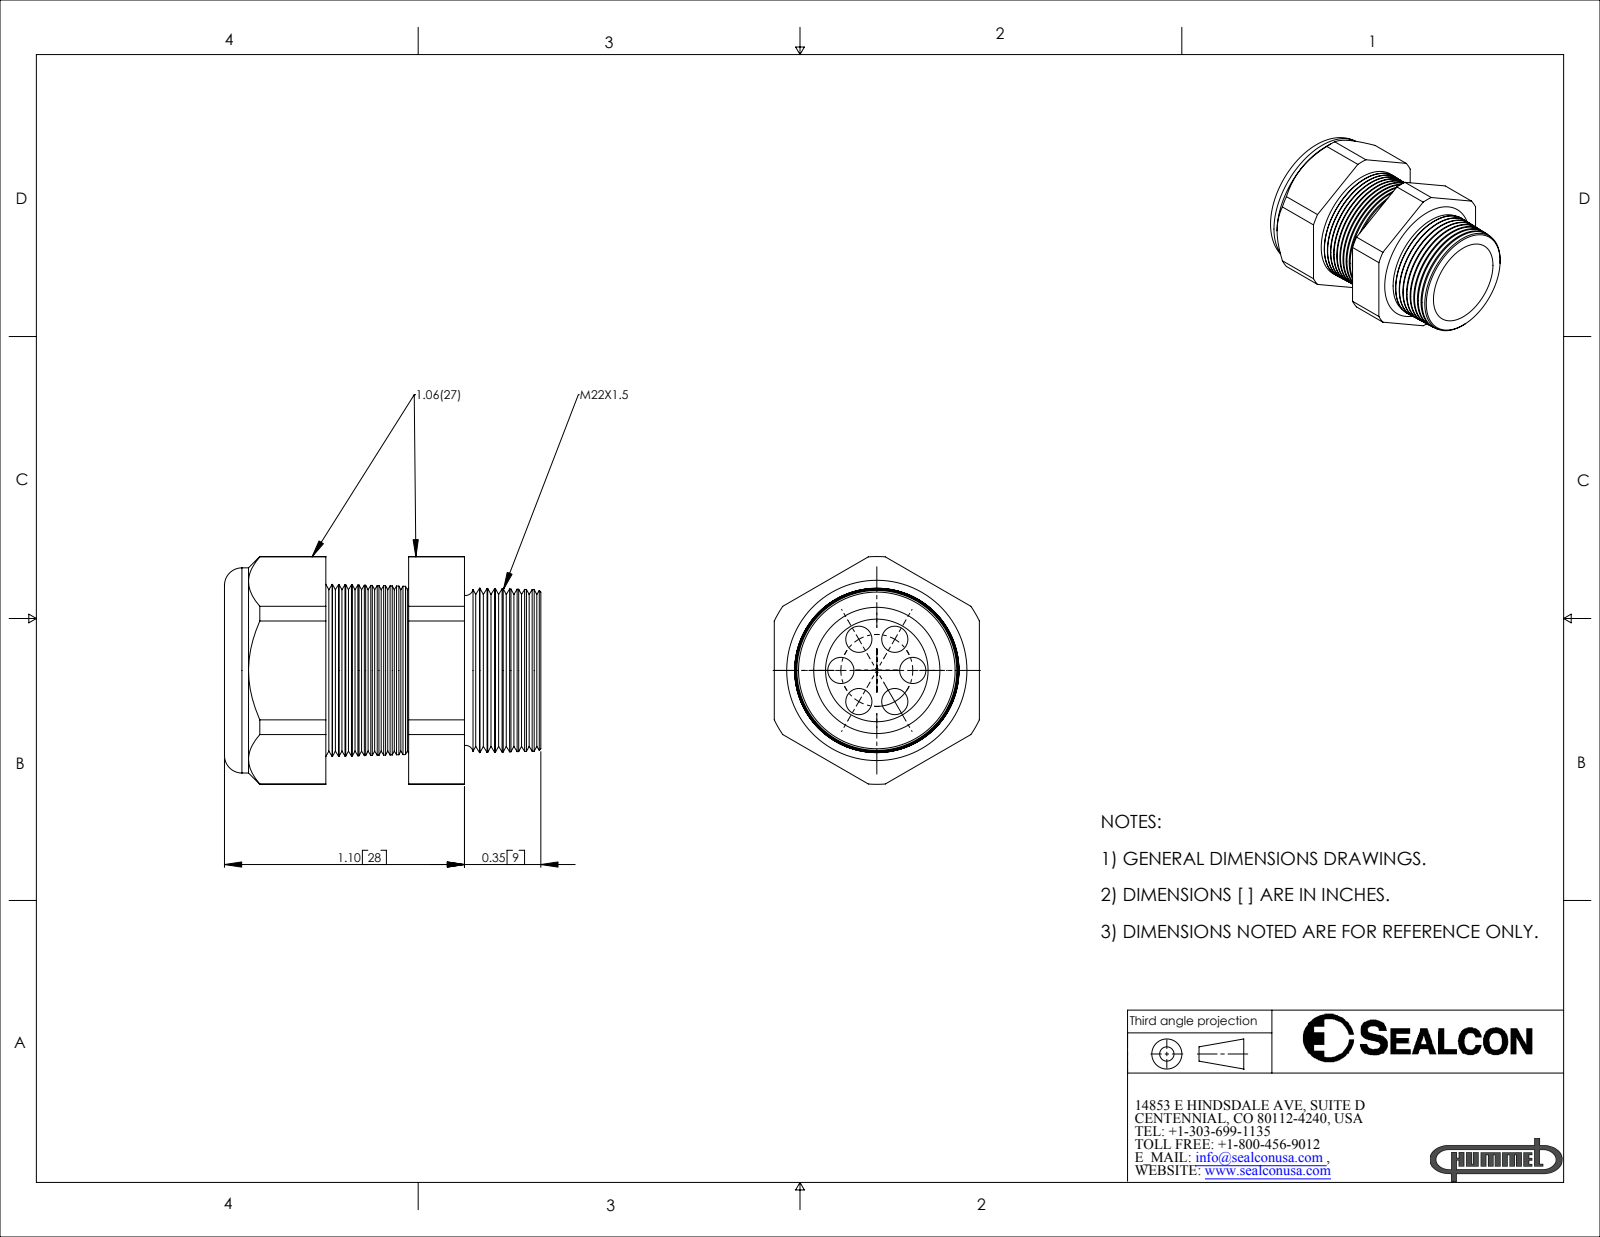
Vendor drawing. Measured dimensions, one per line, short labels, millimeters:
name: CD22M8-BK
written by: SolidWorks 2007 (CONFIG_CONTROL_DESIGN)
unit: mm
bodies: 2 solids, 198 faces (20 planar, 32 cylindrical, 146 other)
size: 36.8 × 26.5 × 23.9
volume: 9 490 mm³; area: 6 716 mm²
holes: 6× ⌀3, 1× ⌀11.4, 1× ⌀11.9
bosses: 1× ⌀23.9
rounds: 1× R13.3
face distances: 23.9, 21.4, 11.8, 9.7, 27.9, 16.1, 6.5, 36.8, 25, 15.4
hole spacings: 4.2, 7.2, 8.4
